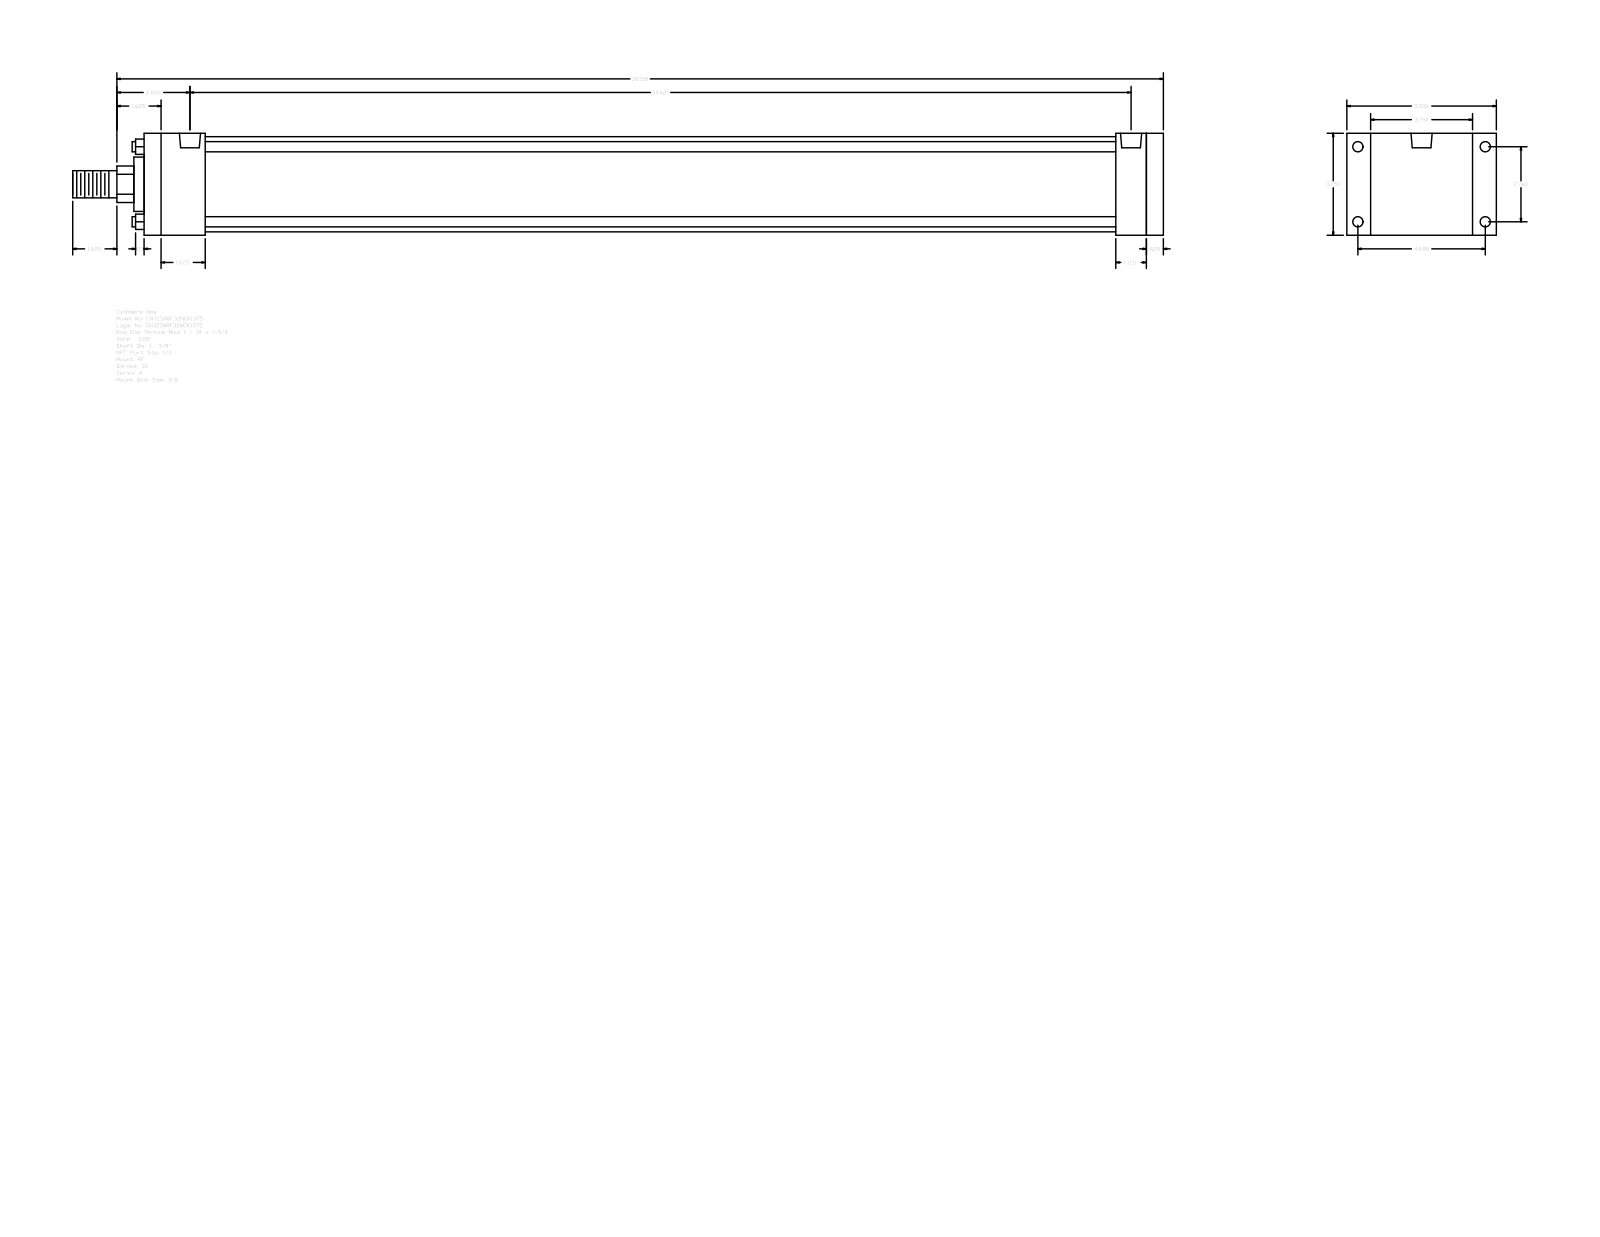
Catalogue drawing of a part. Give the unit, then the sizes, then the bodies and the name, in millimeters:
Units: millimetres
Overall size (bounding box): 1019.17 × 139.7 × 95.25
Round holes (diameter × count): ⌀8.73 ×4, ⌀9.53 ×4, ⌀19.77 ×2
Round bosses / shafts (diameter × count): ⌀9.53 ×4, ⌀88.9 ×1, ⌀50.8 ×1, ⌀34.92 ×1, ⌀25.4 ×1
Partial cylindrical surfaces — rounded edges, fillets, slot ends (radius × count): R17.06 ×1
Main face-to-face distances: 95.24, 952.5, 15.88, 936.62, 57.15, 22.23, 117.47, 908.05, 28.57, 44.45
Hole centre spacings: 3.18, 70.1, 119.06, 138.16, 873.12, 876.3, 879.48
Bodies: 0 solids, 92 faces (64 planar, 28 cylindrical, 0 other)
Part name (STEP PRODUCT): A_RF__0325_1.375
STEP written by: GSSL Pune (CONFIG_CONTROL_DESIGN)
